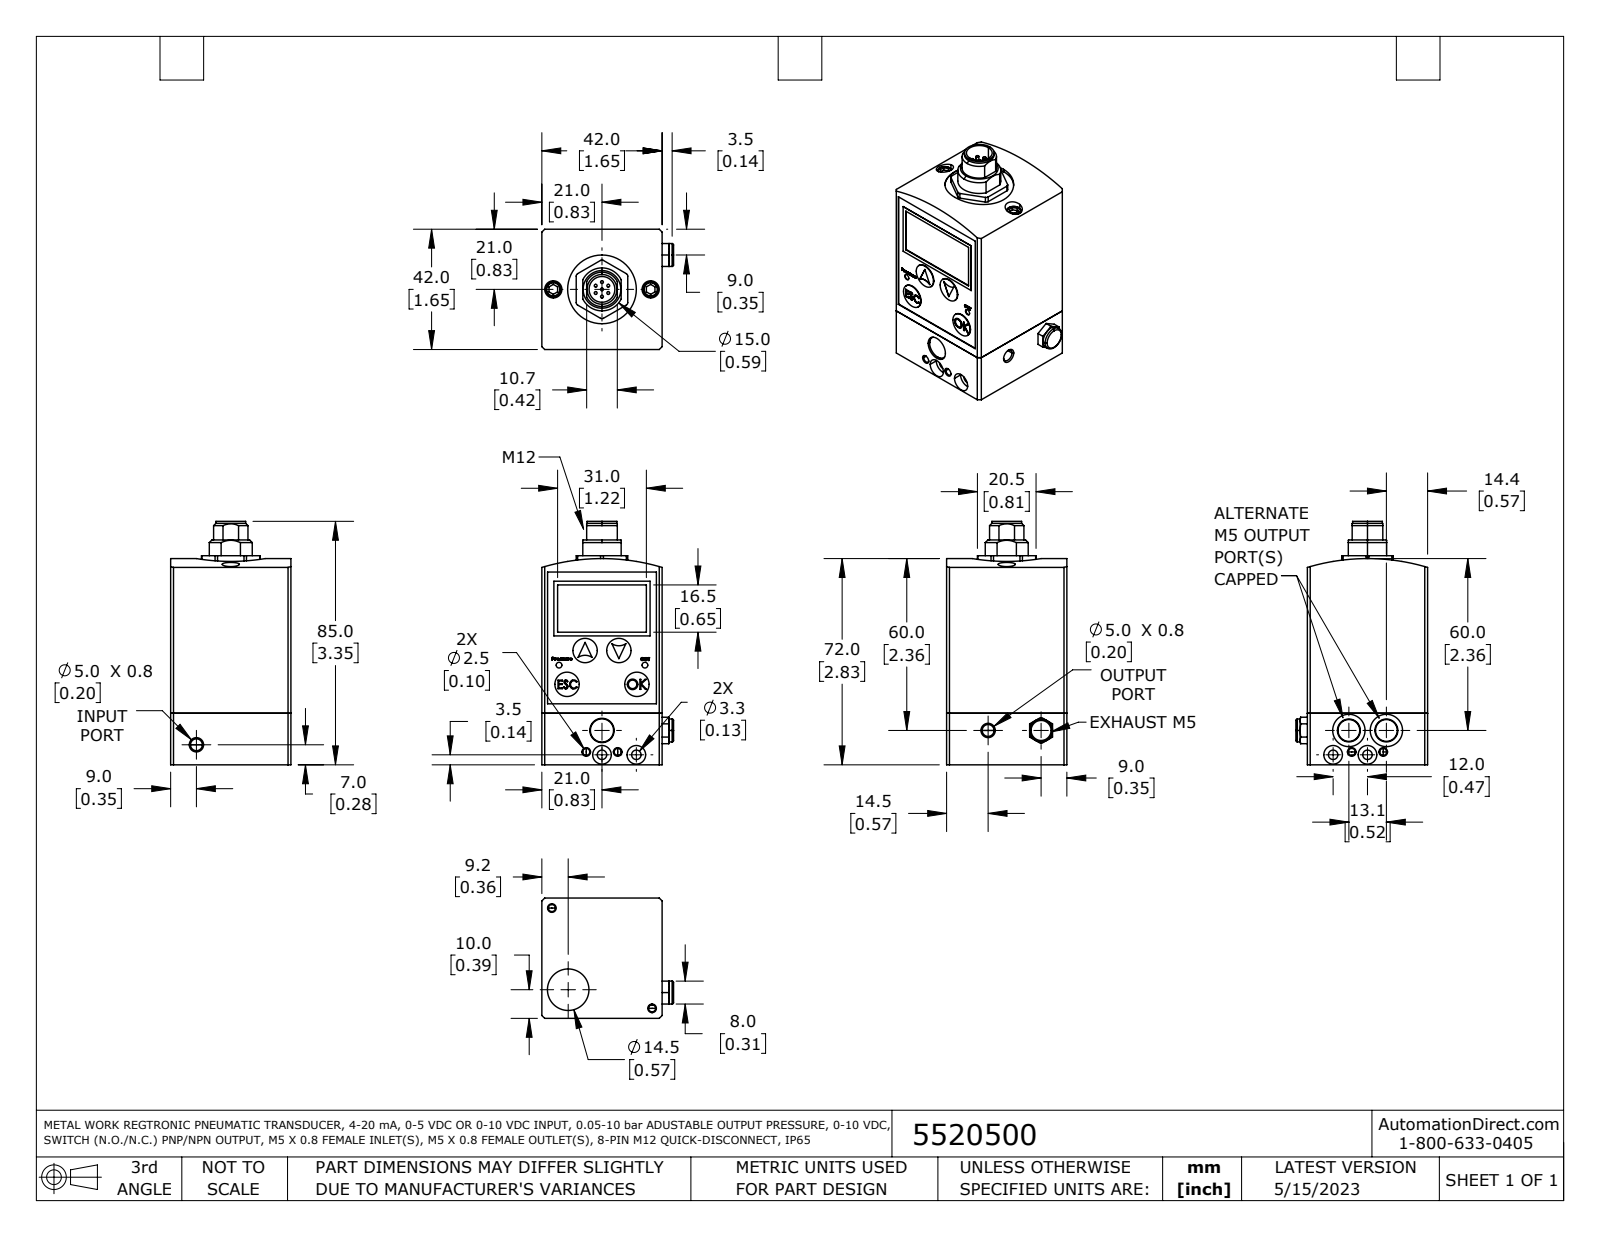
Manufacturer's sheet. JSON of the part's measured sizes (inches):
{"part_name": "5520500", "step_written_by": "SolidWorks 2021 (AUTOMOTIVE_DESIGN)", "units": "inches", "bodies": {"solids": 2, "faces": 498, "planar": 201, "cylindrical": 239, "other": 58}, "overall_size": [3.346, 1.811, 1.654], "volume_in3": 7.576, "surface_area_in2": 33.93, "round_holes": [[0.03, 2], [0.079, 2], [0.097, 2], [0.097, 2], [0.13, 2], [0.163, 2], [0.236, 2], [0.256, 2], [0.445, 2], [0.041, 1], [0.145, 1], [0.335, 1]], "round_bosses_or_shafts": [[0.039, 7], [0.335, 4], [0.315, 3], [0.197, 2], [0.023, 2], [0.409, 1], [0.117, 1], [0.033, 1]], "partial_cylinders_radius": [[0.039, 6], [0.006, 4], [0.009, 3], [0.004, 2], [0.004, 2], [0.005, 2], [0.005, 2], [0.007, 2]], "face_to_face_distances": [1.654, 0.709, 1.646, 1.638, 0.016, 0.118, 0.079, 2.283, 0.02, 1.653], "hole_center_spacings": [0.22, 0.366, 0.669, 0.689, 0.974, 1.074, 1.126, 1.25]}
